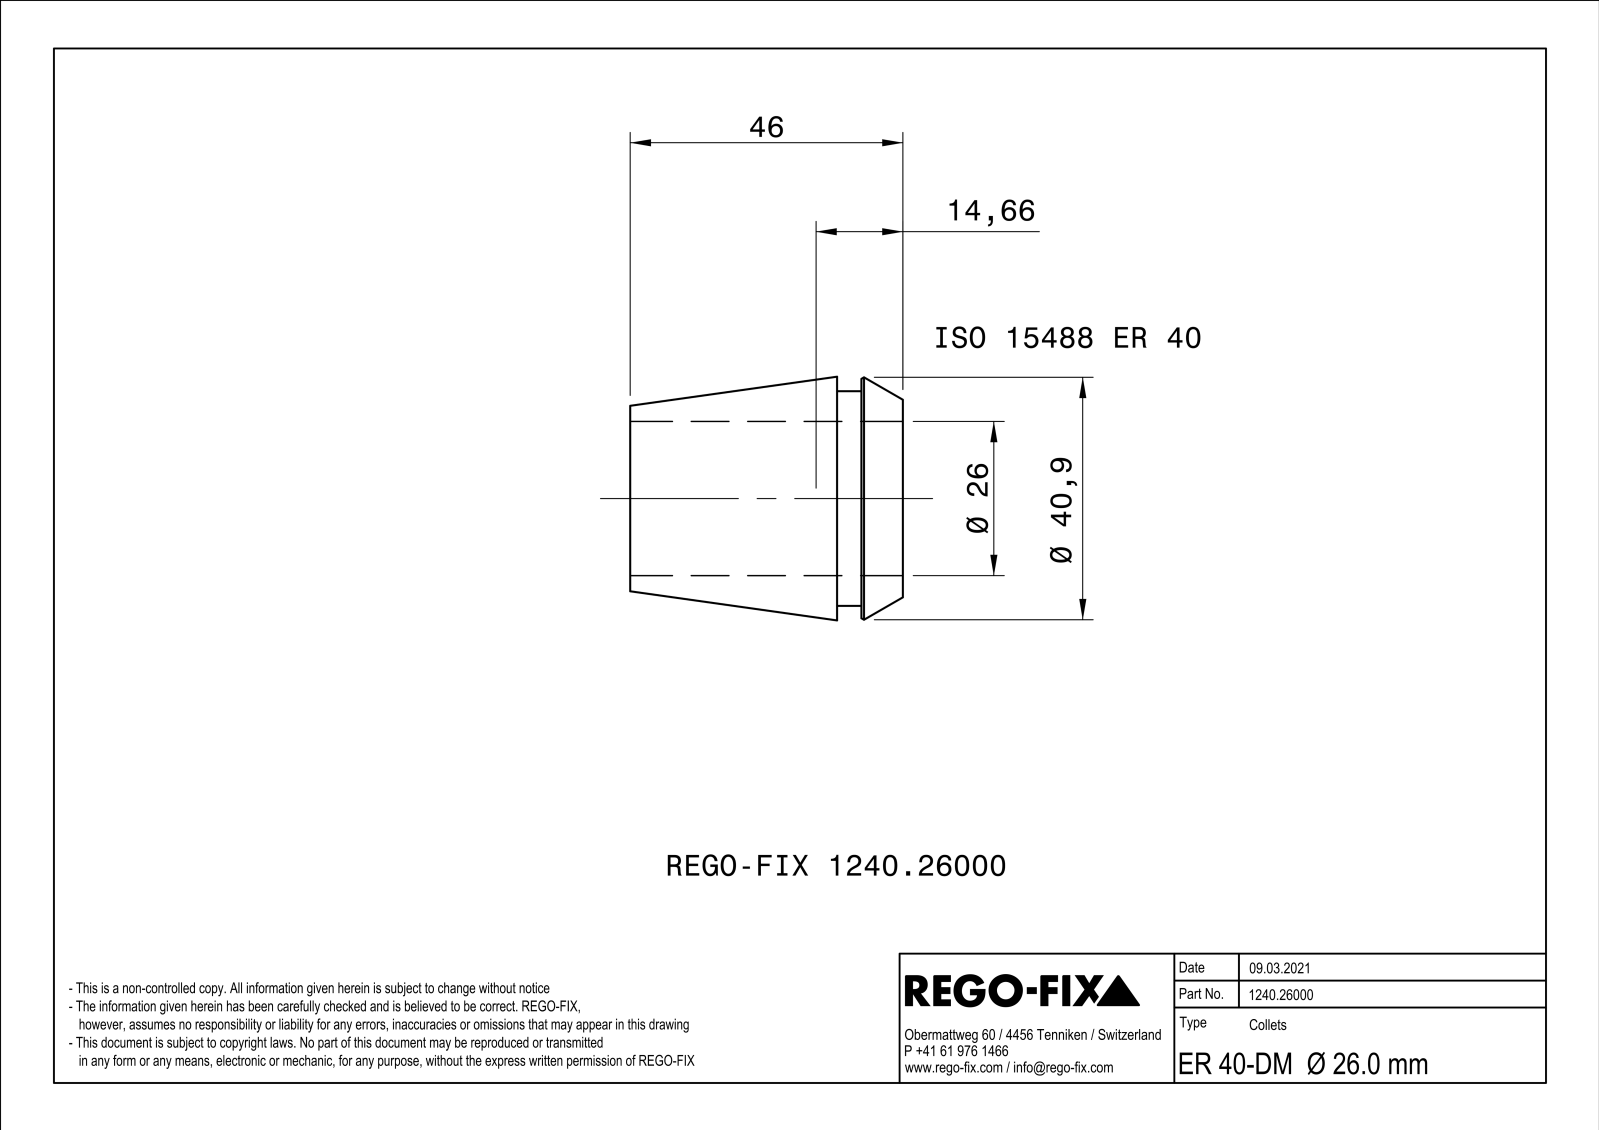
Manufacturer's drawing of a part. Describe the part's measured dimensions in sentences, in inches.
The part is named "NOCUT". Its 3-D file was written by "SIEMENS PLM Software Solid Edge ST10 (AUTOMOTIVE_DESIGN)". It is 1 solid with 154 faces: 80 planar, 9 cylindrical and 65 other. Overall it measures 1.811 by 1.614 by 1.614 inches. Its volume is 1.255 cubic inches and its surface area 22.94 square inches. Round holes: 1 of diameter 1.024. Round bosses or shafts: 1 of diameter 1.425. The main face-to-face distances are 0.039, 0.437, 0.276, 0.161, 1.811, 1.535, 1.374, 0.669, 0.394, 0.232.
